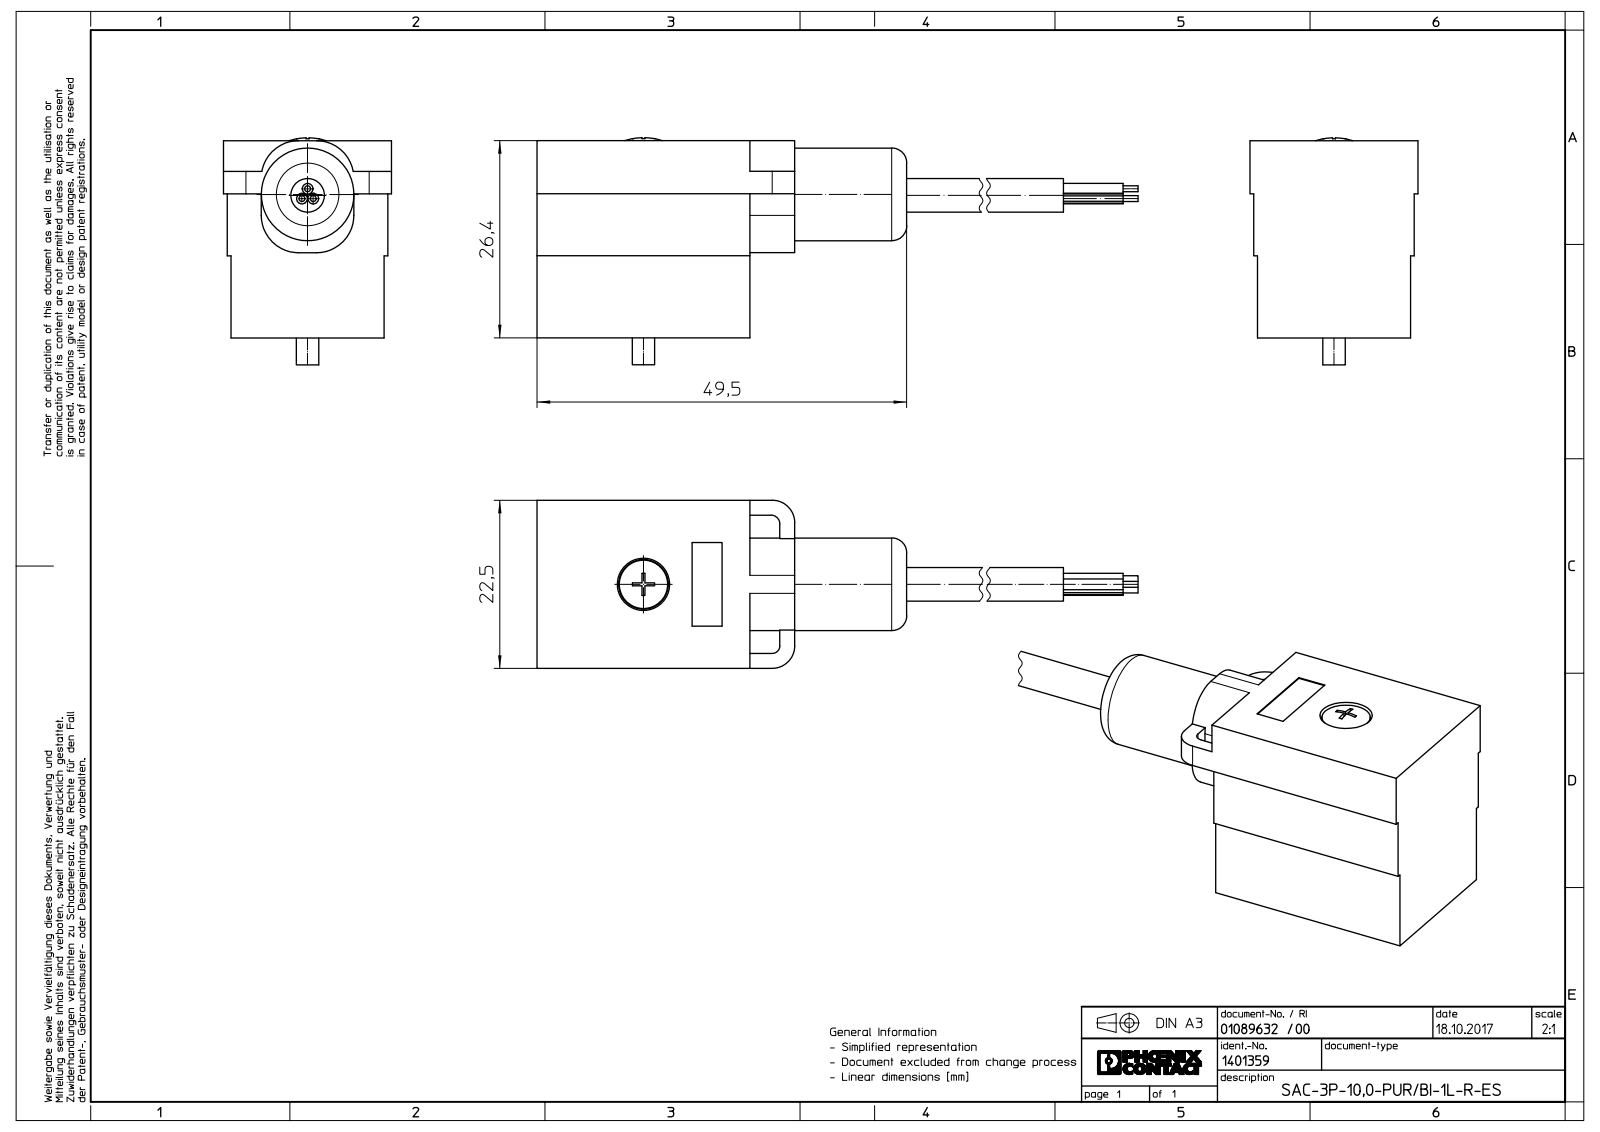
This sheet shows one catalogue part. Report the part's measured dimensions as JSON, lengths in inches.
{"part_name": "5814-1 Actuator cable - SAC-3P- 10,0-PURBI-1L-R-ES - 1401359; 5814 Actuator cable - SAC-3P- 10,0-PURBI-1L-R-ES - 1401359", "step_written_by": "Alibre (AUTOMOTIVE_DESIGN)", "units": "inches", "bodies": {"solids": 1, "faces": 132, "planar": 93, "cylindrical": 33, "other": 6}, "overall_size": [6.28, 1.196, 0.886], "volume_in3": 1.206, "surface_area_in2": 10.8, "round_holes": [[0.24, 1], [0.276, 1]], "round_bosses_or_shafts": [[0.031, 3], [0.056, 2], [0.488, 1], [0.177, 1], [0.118, 1]], "partial_cylinders_radius": [[0.197, 4], [0.118, 2], [0.028, 1], [0.039, 1], [0.046, 1]], "face_to_face_distances": [0.02, 0.846, 0.827, 0.039, 0.866, 1.122, 0.98, 0.807, 0.886, 0.059]}
